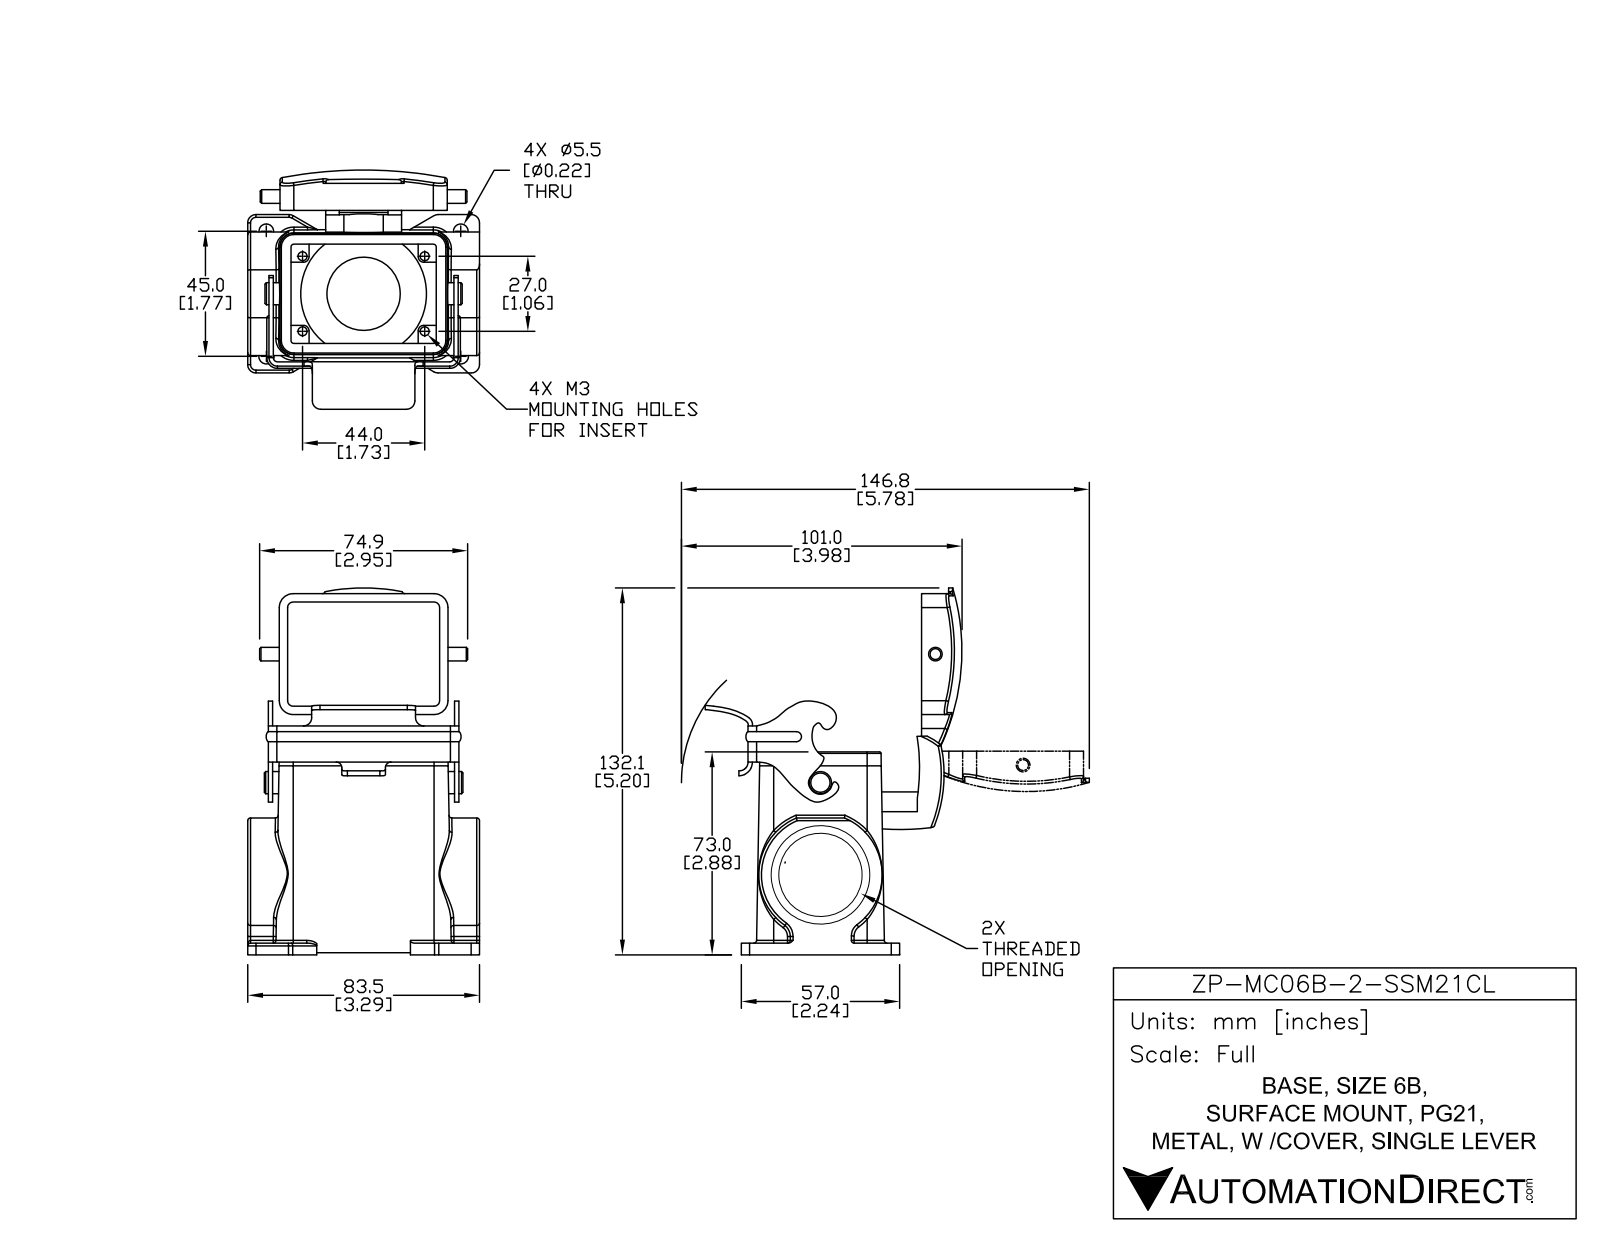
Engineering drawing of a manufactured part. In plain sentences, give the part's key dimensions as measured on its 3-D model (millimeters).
The part is named "ZP-MC06B-2-SSM29CL". Its 3-D file was written by "SolidWorks 2014 (AUTOMOTIVE_DESIGN)". It is 3 solids with 401 faces: 153 planar, 134 cylindrical and 114 other. Overall it measures 135.62 by 83.5 by 81.84 millimeters. Its volume is 132 736 cubic millimeters and its surface area 59 297 square millimeters. Round holes: 4 of diameter 3, 4 of diameter 5.5, 1 of diameter 25.23, 1 of diameter 30, 1 of diameter 35.5. Round bosses or shafts: 1 of diameter 7.95, 1 of diameter 5. Partial cylindrical surfaces (rounded edges, fillets, slot ends): 26 of radius 1, 12 of radius 3, 8 of radius 2, 6 of radius 5, 4 of radius 0.5, 4 of radius 6, 2 of radius 1.5, 2 of radius 3.06. The main face-to-face distances are 39.67, 1.56, 56.35, 0.5, 3, 73.5, 8.15, 10.19, 73.31, 8.63. The hole center spacings are 15.81, 25.81, 38.28, 41.61, 57.71, 67.42, 27, 44.
